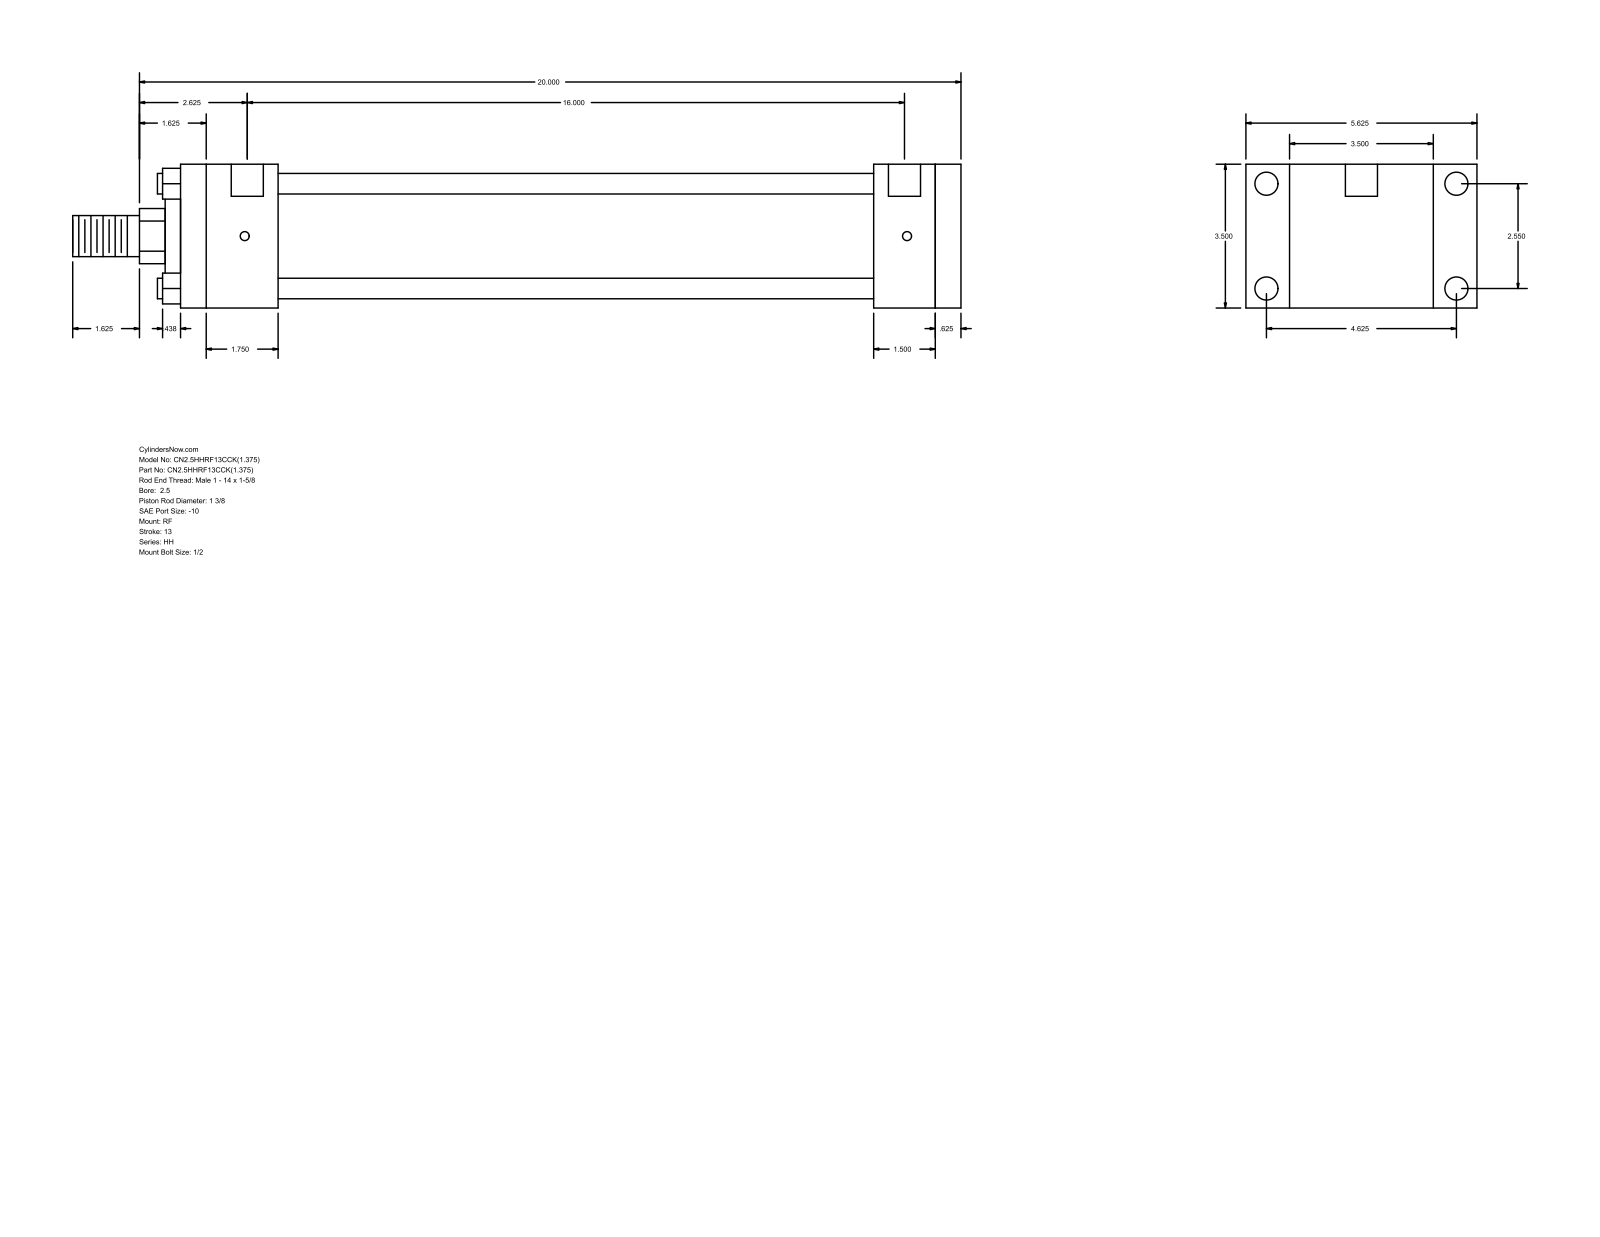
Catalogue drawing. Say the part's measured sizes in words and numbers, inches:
The part is named "HH_RF__0250_1.375". Its 3-D file was written by "GSSL Pune (CONFIG_CONTROL_DESIGN)". It is 0 solids with 92 faces: 64 planar, 28 cylindrical and 0 other. Overall it measures 21.625 by 5.625 by 3.5 inches. Round holes: 4 of diameter 0.219, 4 of diameter 0.563, 2 of diameter 0.781. Round bosses or shafts: 4 of diameter 0.5, 1 of diameter 2.875, 1 of diameter 2, 1 of diameter 1.375, 1 of diameter 1. Partial cylindrical surfaces (rounded edges, fillets, slot ends): 1 of radius 0.672. The main face-to-face distances are 3.5, 19, 0.625, 18.375, 2.375, 16, 16.625, 16.875, 14.5, 1.5. The hole center spacings are 2.55, 4.625, 5.281, 16.125, 0.062, 0.063, 16, 16.062.
